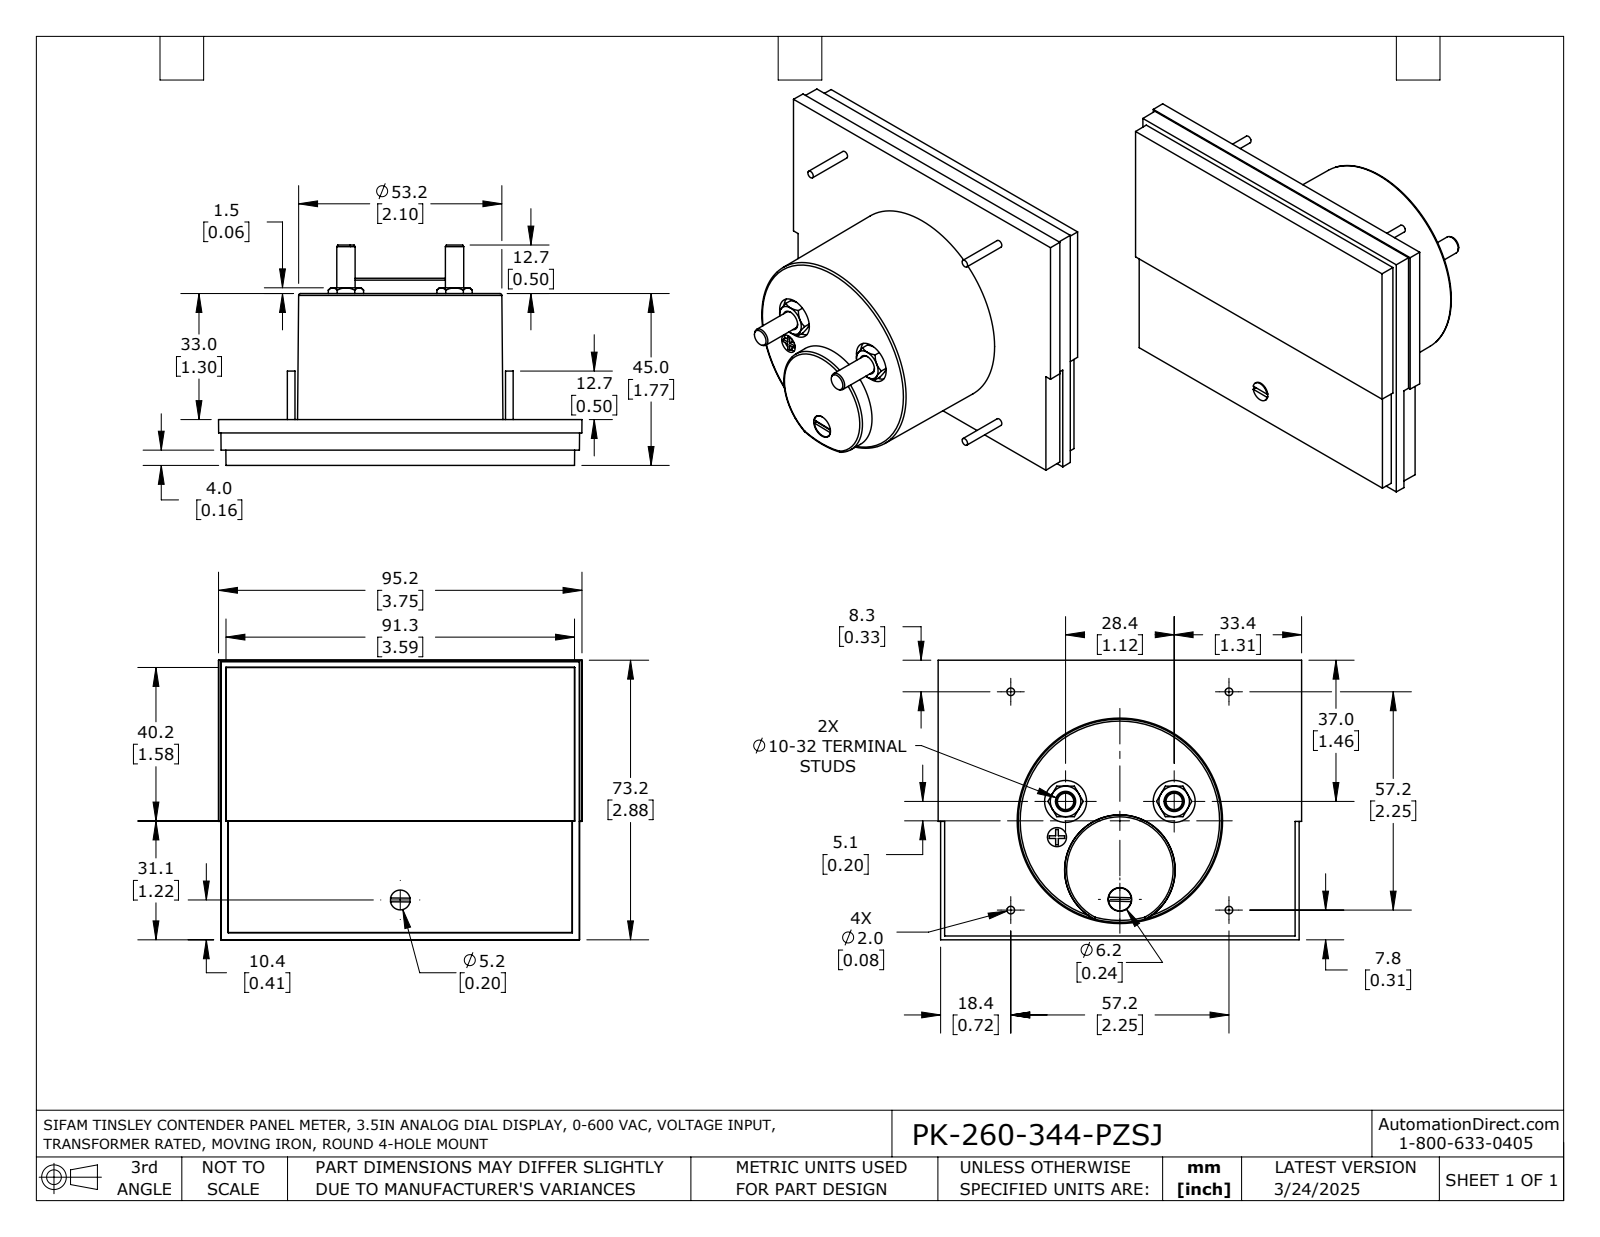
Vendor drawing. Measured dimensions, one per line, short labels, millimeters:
name: PK-260-344-PZSJ
written by: SolidWorks 2021 (AUTOMOTIVE_DESIGN)
unit: mm
bodies: 1 solid, 163 faces (76 planar, 31 cylindrical, 56 other)
size: 95.2 × 73.2 × 57.7
volume: 154 800 mm³; area: 24 770 mm²
holes: 2× ⌀11, 1× ⌀5, 1× ⌀6.2
bosses: 4× ⌀2, 2× ⌀4.8, 1× ⌀6, 1× ⌀5.2
rounds: 1× R2.5
face distances: 12, 0.8, 11.3, 45, 33, 44.2, 4, 1.9, 8, 37
hole spacings: 29.3, 9.6, 23.2, 28.4, 32.1
